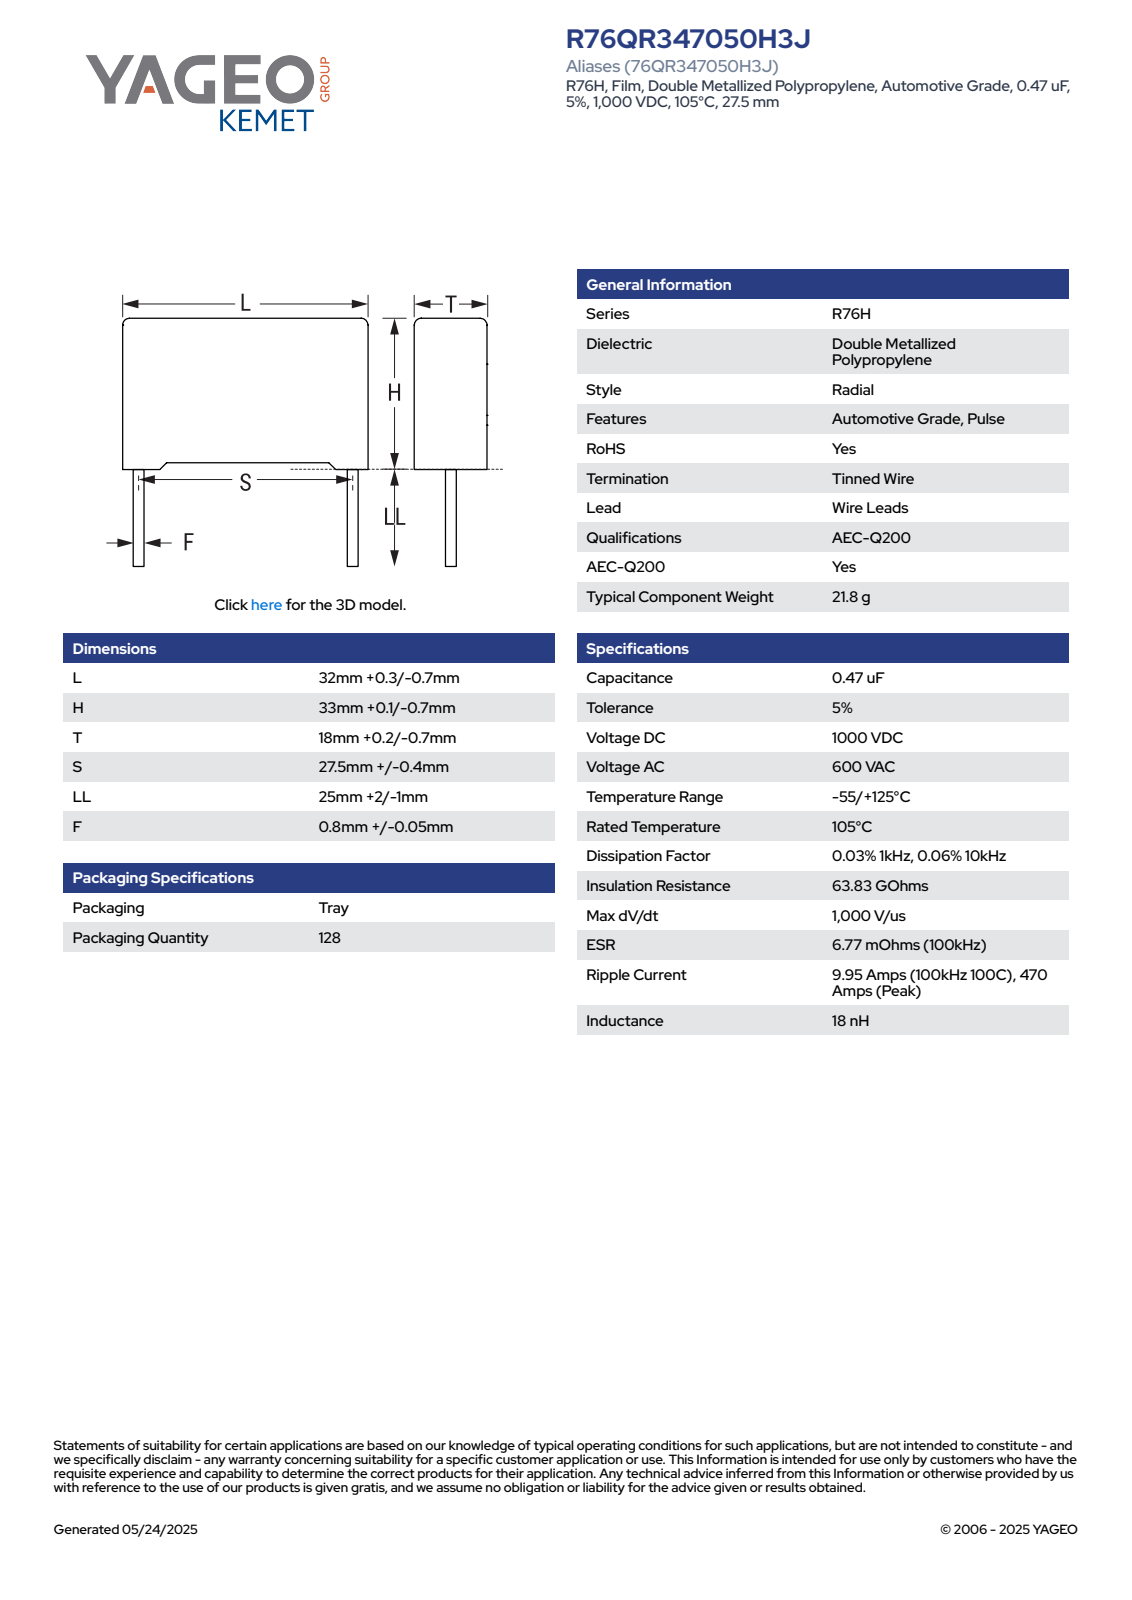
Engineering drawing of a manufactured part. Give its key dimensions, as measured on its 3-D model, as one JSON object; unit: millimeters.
{"part_name": "CFR_RB2R76_32X33X18_L32.3H33.1T18.2S27.5LL27F0.85", "step_written_by": "SolidWorks 2014 (AUTOMOTIVE_DESIGN)", "units": "millimeters", "bodies": {"solids": 4, "faces": 85, "planar": 77, "cylindrical": 8, "other": 0}, "overall_size": [60.1, 32.3, 18.2], "volume_mm3": 18919, "surface_area_mm2": 4711, "round_bosses_or_shafts": [[0.85, 2]], "partial_cylinders_radius": [[0.5, 4]], "face_to_face_distances": [18.2, 32.3, 31.96, 0.39, 32.35, 0.75, 1.14, 33.1, 1.08, 31.22]}
